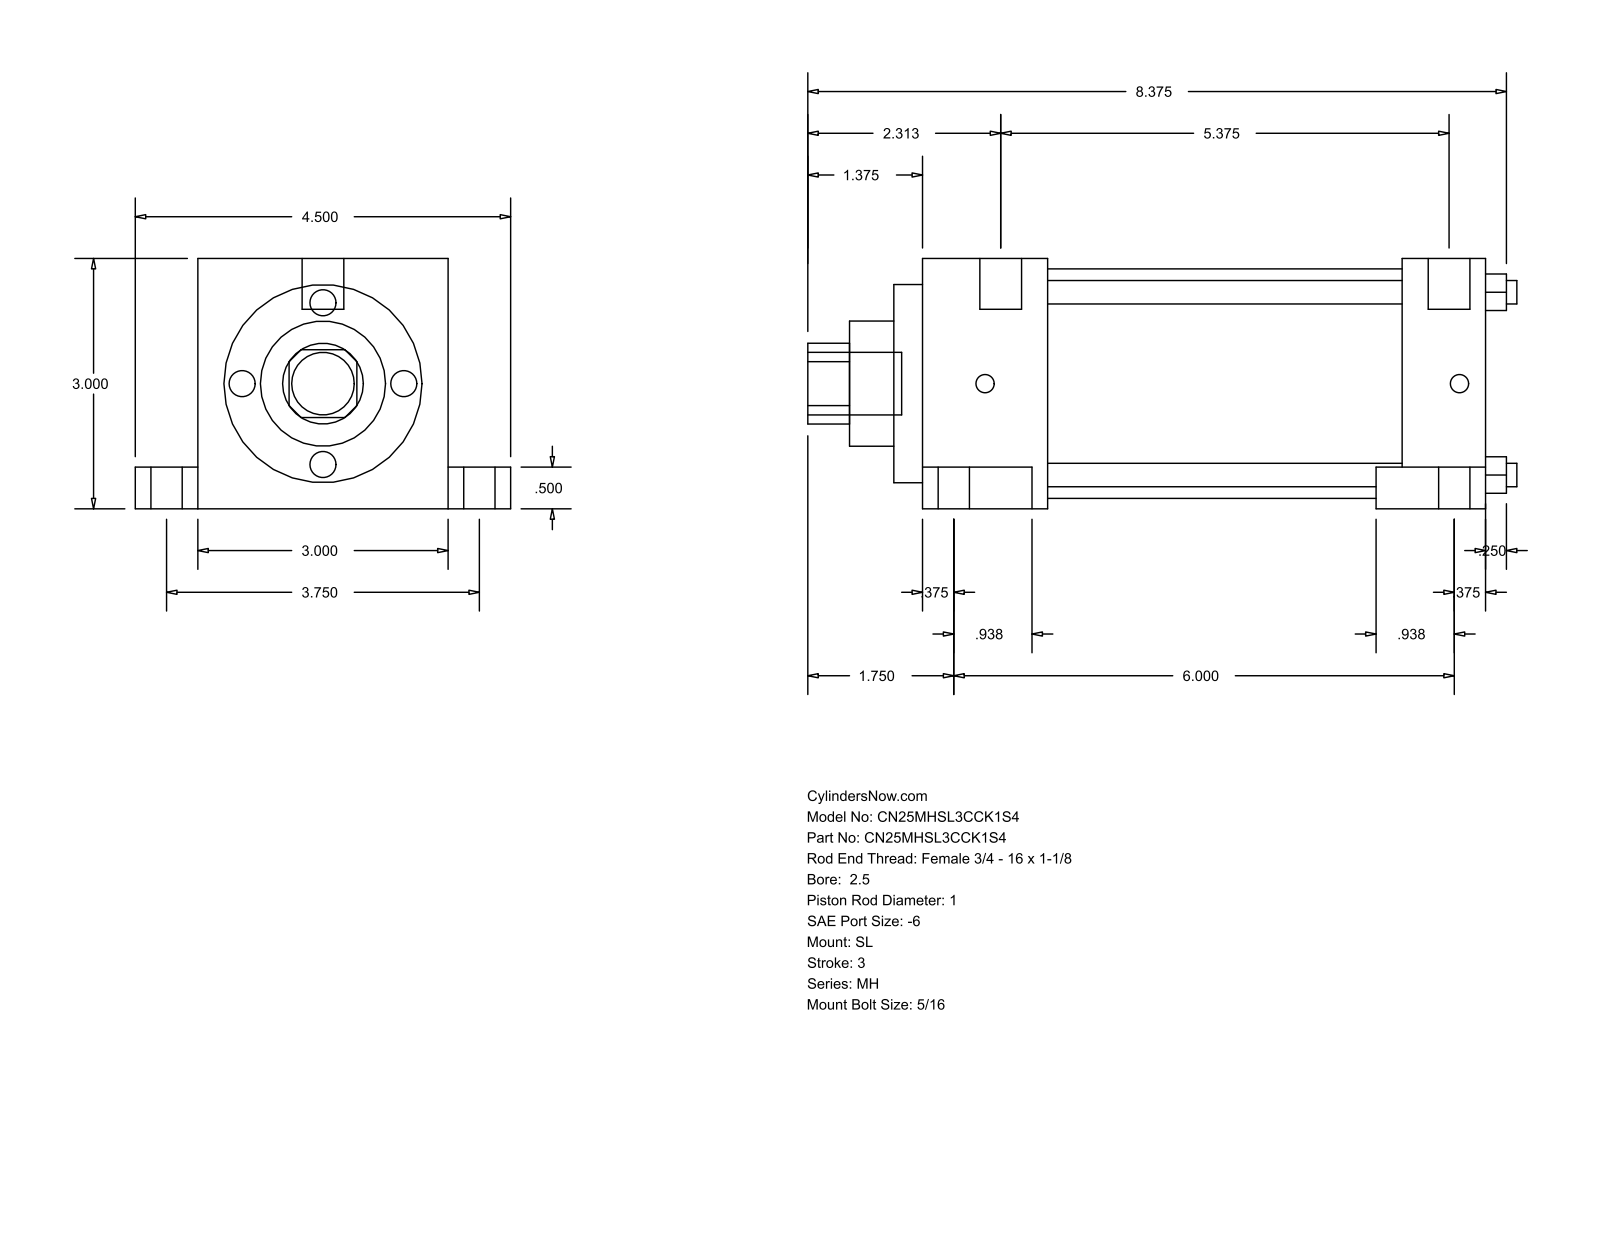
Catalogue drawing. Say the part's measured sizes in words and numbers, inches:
The part is named "MH_SL__0250_1". Its 3-D file was written by "GSSL Pune (CONFIG_CONTROL_DESIGN)". It is 0 solids with 86 faces: 61 planar, 25 cylindrical and 0 other. Overall it measures 8.5 by 4.5 by 3 inches. Round holes: 4 of diameter 0.281, 1 of diameter 1, 1 of diameter 1.5, 1 of diameter 2.375, 1 of diameter 2.75. Round bosses or shafts: 2 of diameter 0.625, 2 of diameter 0.375, 2 of diameter 0.219, 1 of diameter 0.75, 1 of diameter 0.5. Partial cylindrical surfaces (rounded edges, fillets, slot ends): 1 of radius 0.484. The main face-to-face distances are 3, 1, 6.094, 7.094, 0.5, 2.5, 0.75, 3.75, 0.531, 6.625. The hole center spacings are 1.548, 2.19, 3.097.
